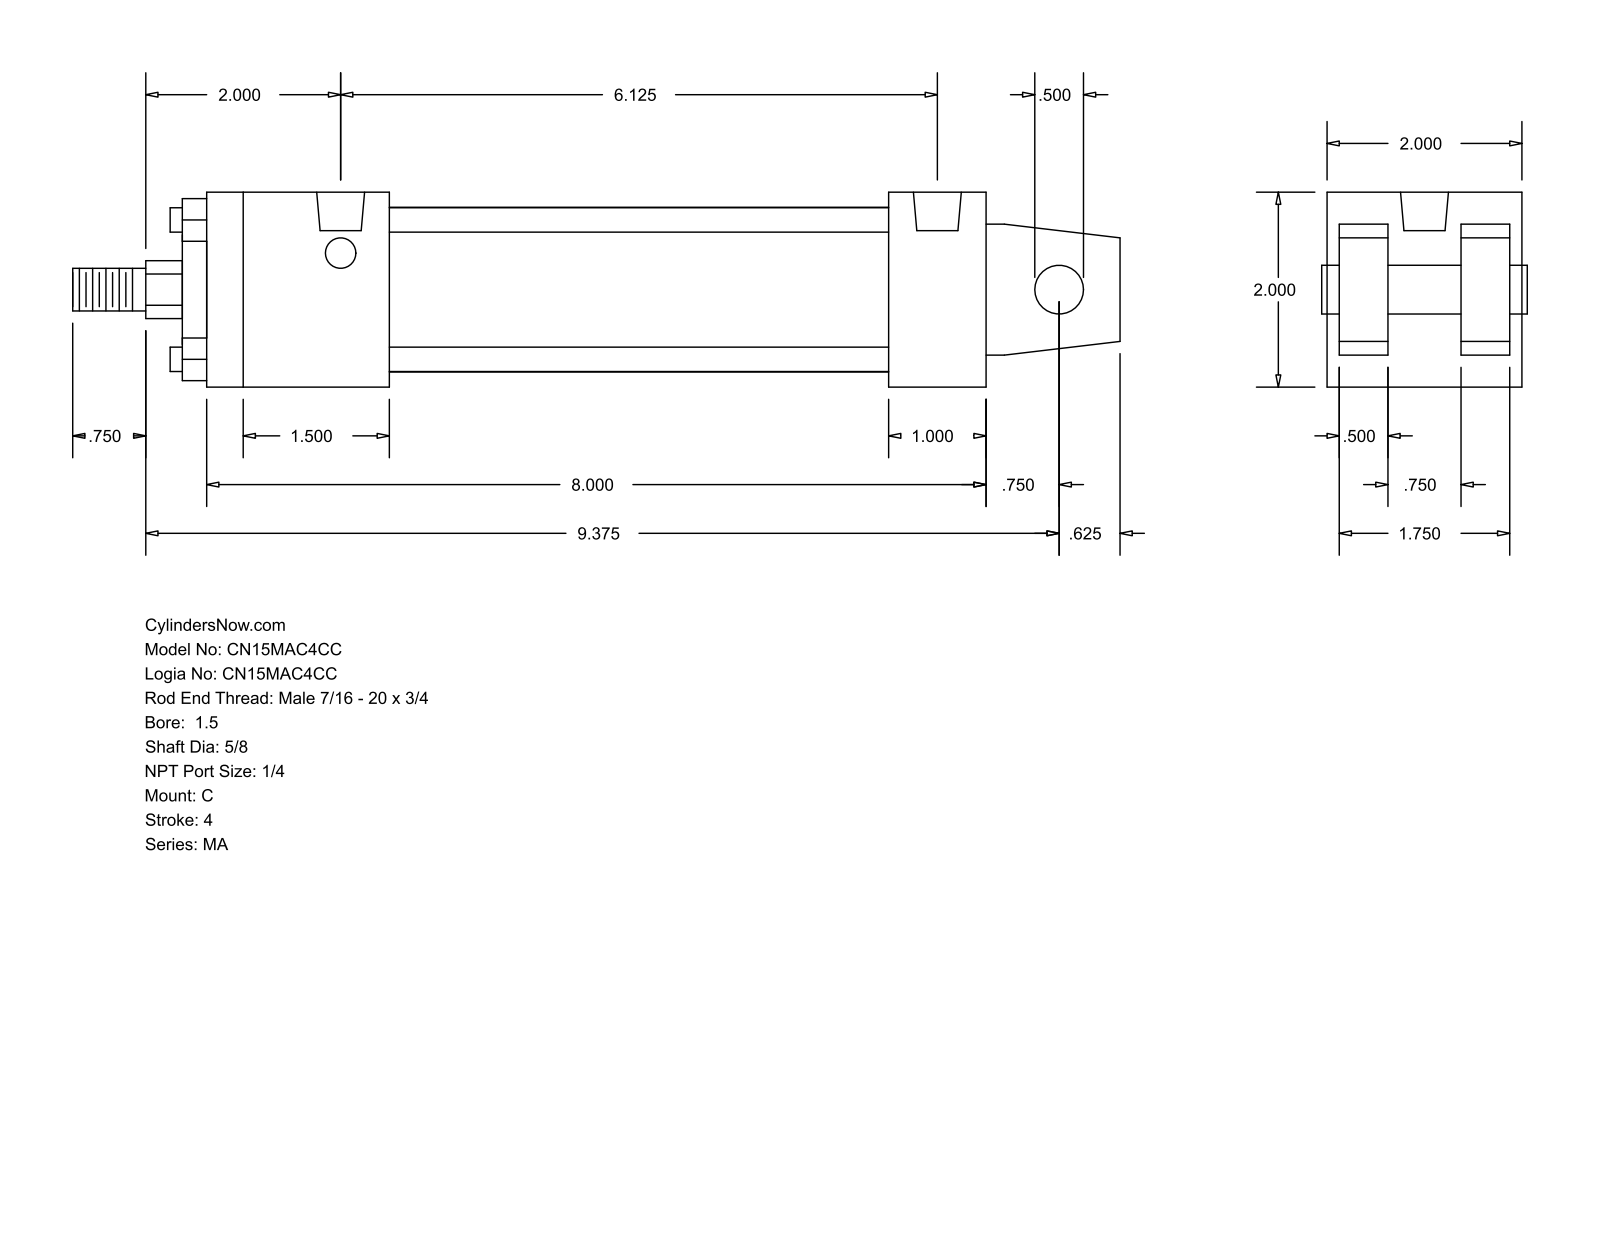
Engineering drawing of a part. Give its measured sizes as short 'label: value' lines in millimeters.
name: MA_C__0150_0.625
written by: GSSL Pune (CONFIG_CONTROL_DESIGN)
unit: mm
bodies: 0 solids, 103 faces (76 planar, 27 cylindrical, 0 other)
size: 273.05 × 50.8 × 50.8
holes: 4× ⌀7.94, 2× ⌀12.49
bosses: 4× ⌀6.35, 1× ⌀42.93, 1× ⌀28.57, 1× ⌀15.88, 1× ⌀12.7, 1× ⌀11.11
rounds: 1× R7.54
face distances: 50.8, 34.93, 12.7, 15.87, 3.17, 47.63, 31.76, 203.19, 177.8, 25.39
hole spacings: 155.58
